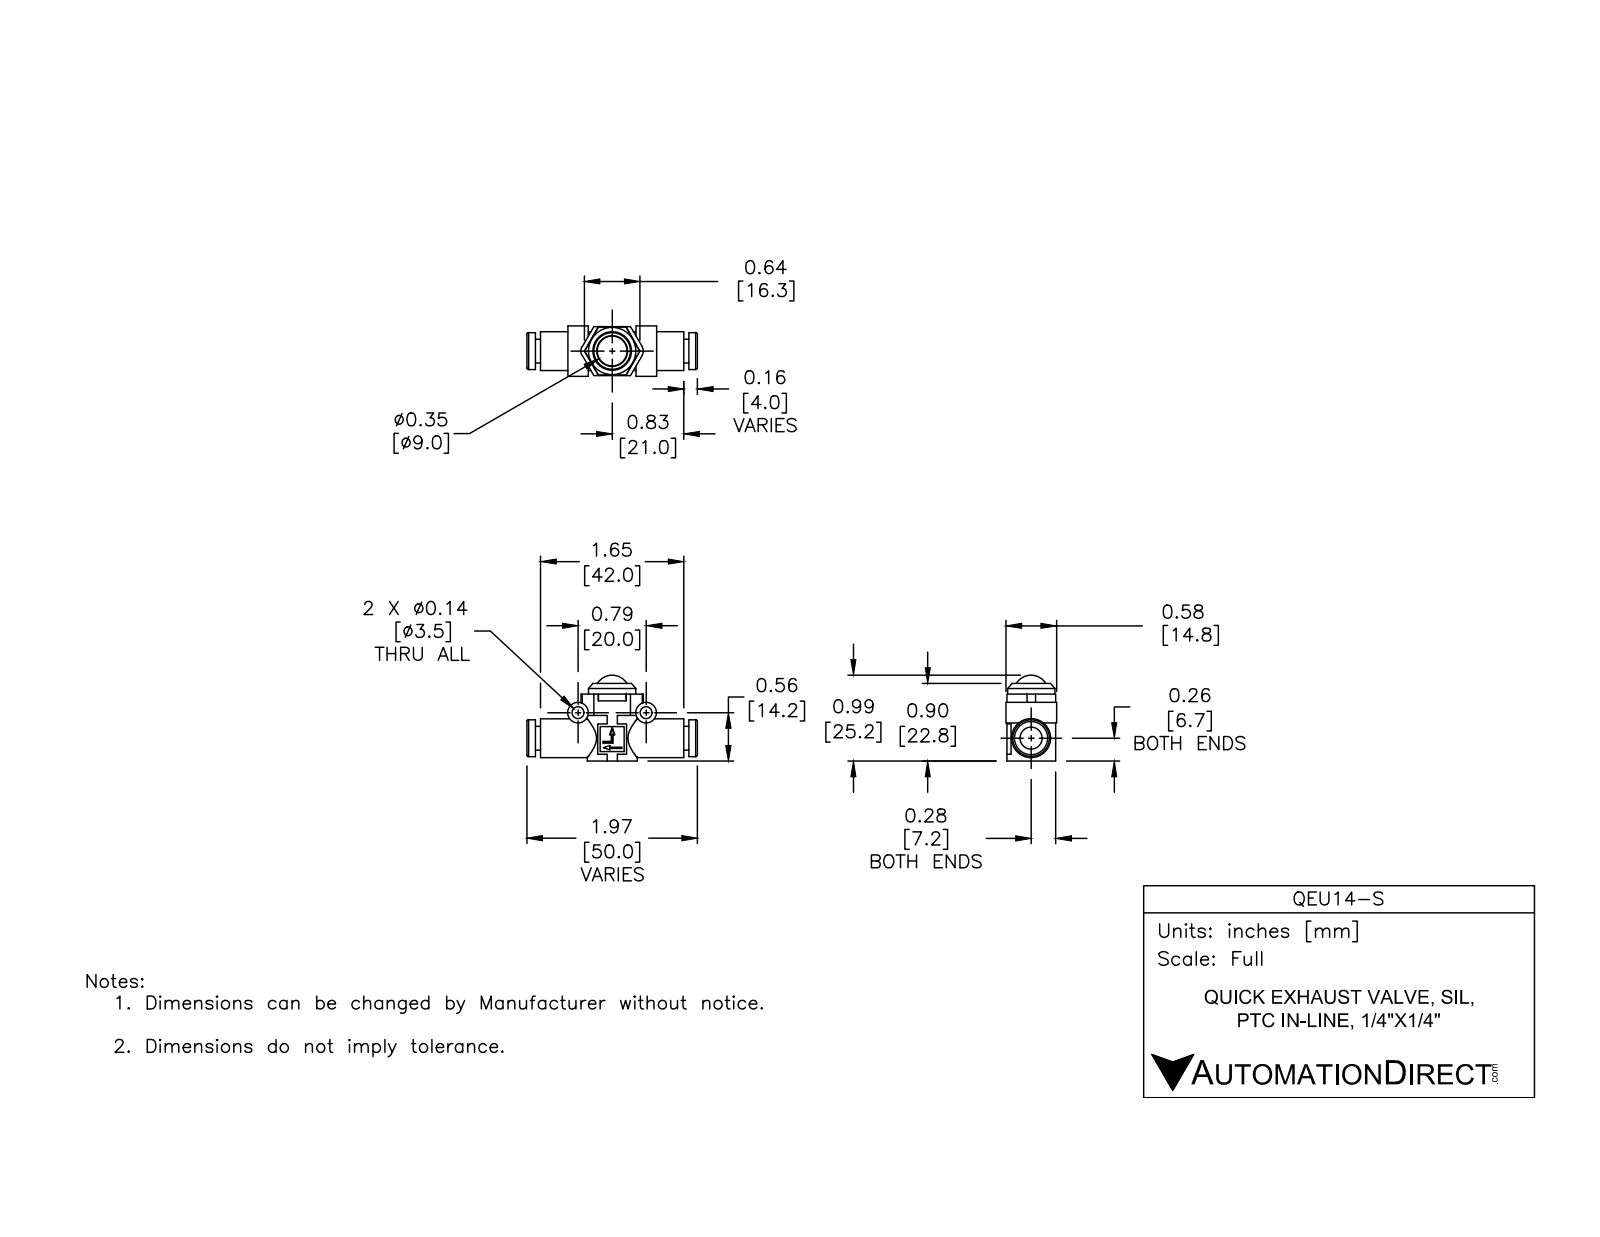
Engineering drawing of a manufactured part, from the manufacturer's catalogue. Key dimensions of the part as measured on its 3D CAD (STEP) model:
Part name (STEP PRODUCT): QEU14-S
STEP written by: SolidWorks 2015 (CONFIG_CONTROL_DESIGN)
Units: millimetres
Bodies: 3 solids, 129 faces (82 planar, 38 cylindrical, 9 other)
Overall size (bounding box): 50 × 25.18 × 14.8
Volume: 6 619 mm³ · Surface area: 5 400 mm²
Round holes (diameter × count): ⌀3.5 ×2, ⌀6.5 ×1, ⌀7.5 ×1, ⌀10.75 ×1
Round bosses / shafts (diameter × count): ⌀6 ×2, ⌀14.65 ×1, ⌀13.82 ×1, ⌀11.4 ×1, ⌀10.8 ×1, ⌀7 ×1
Partial cylindrical surfaces — rounded edges, fillets, slot ends (radius × count): R2.5 ×2
Main face-to-face distances: 1.5, 43.5, 14.34, 2.5, 4, 46, 47.5, 14.57, 16.5, 1.19
Hole centre spacings: 20
